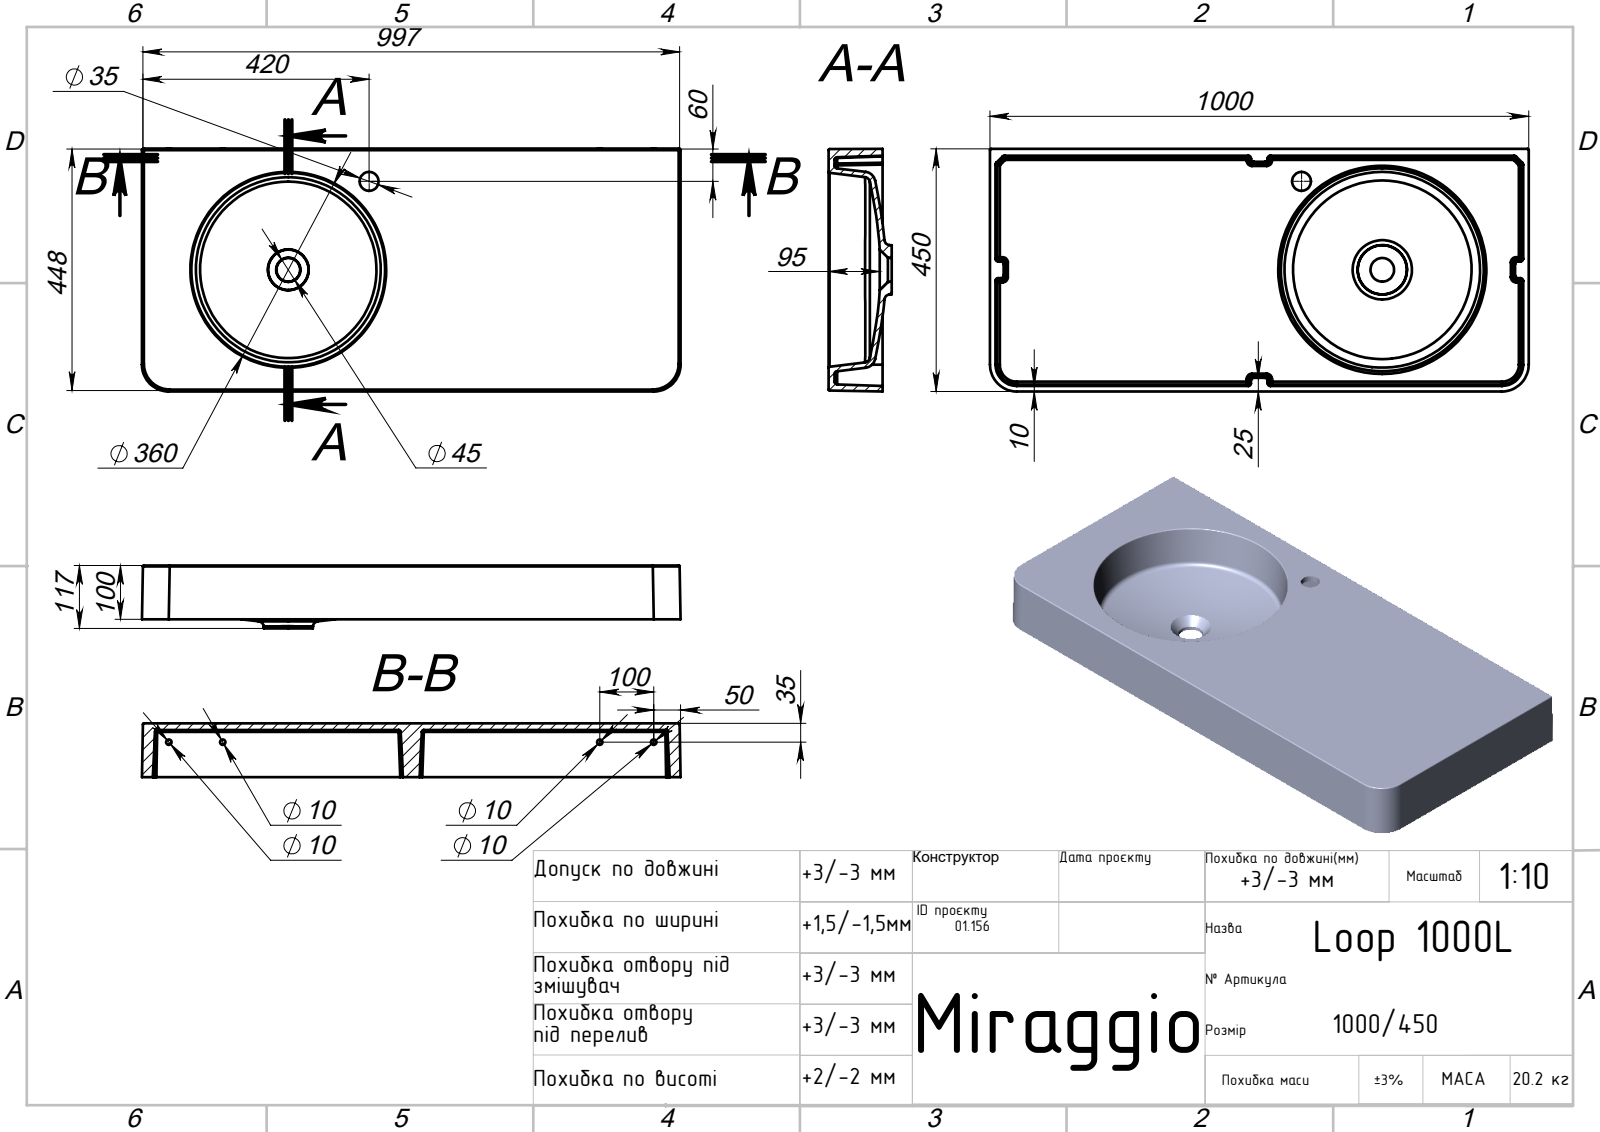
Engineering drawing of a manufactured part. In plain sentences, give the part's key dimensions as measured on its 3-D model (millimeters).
The part is named "Loop 1000L". Its 3-D file was written by "SolidWorks 2020 (AUTOMOTIVE_DESIGN)". It is 1 solid with 126 faces: 31 planar, 55 cylindrical and 40 other. Overall it measures 1000 by 450 by 117 millimeters. Its volume is 8 749 000 cubic millimeters and its surface area 1 557 000 square millimeters. Round holes: 4 of diameter 10, 1 of diameter 35. Partial cylindrical surfaces (rounded edges, fillets, slot ends): 34 of radius 5, 6 of radius 2, 2 of radius 50. The main face-to-face distances are 11, 89, 100, 17, 106, 117, 14.99, 14.98, 11.18, 215.83. The hole center spacings are 100, 800, 700, 900.
